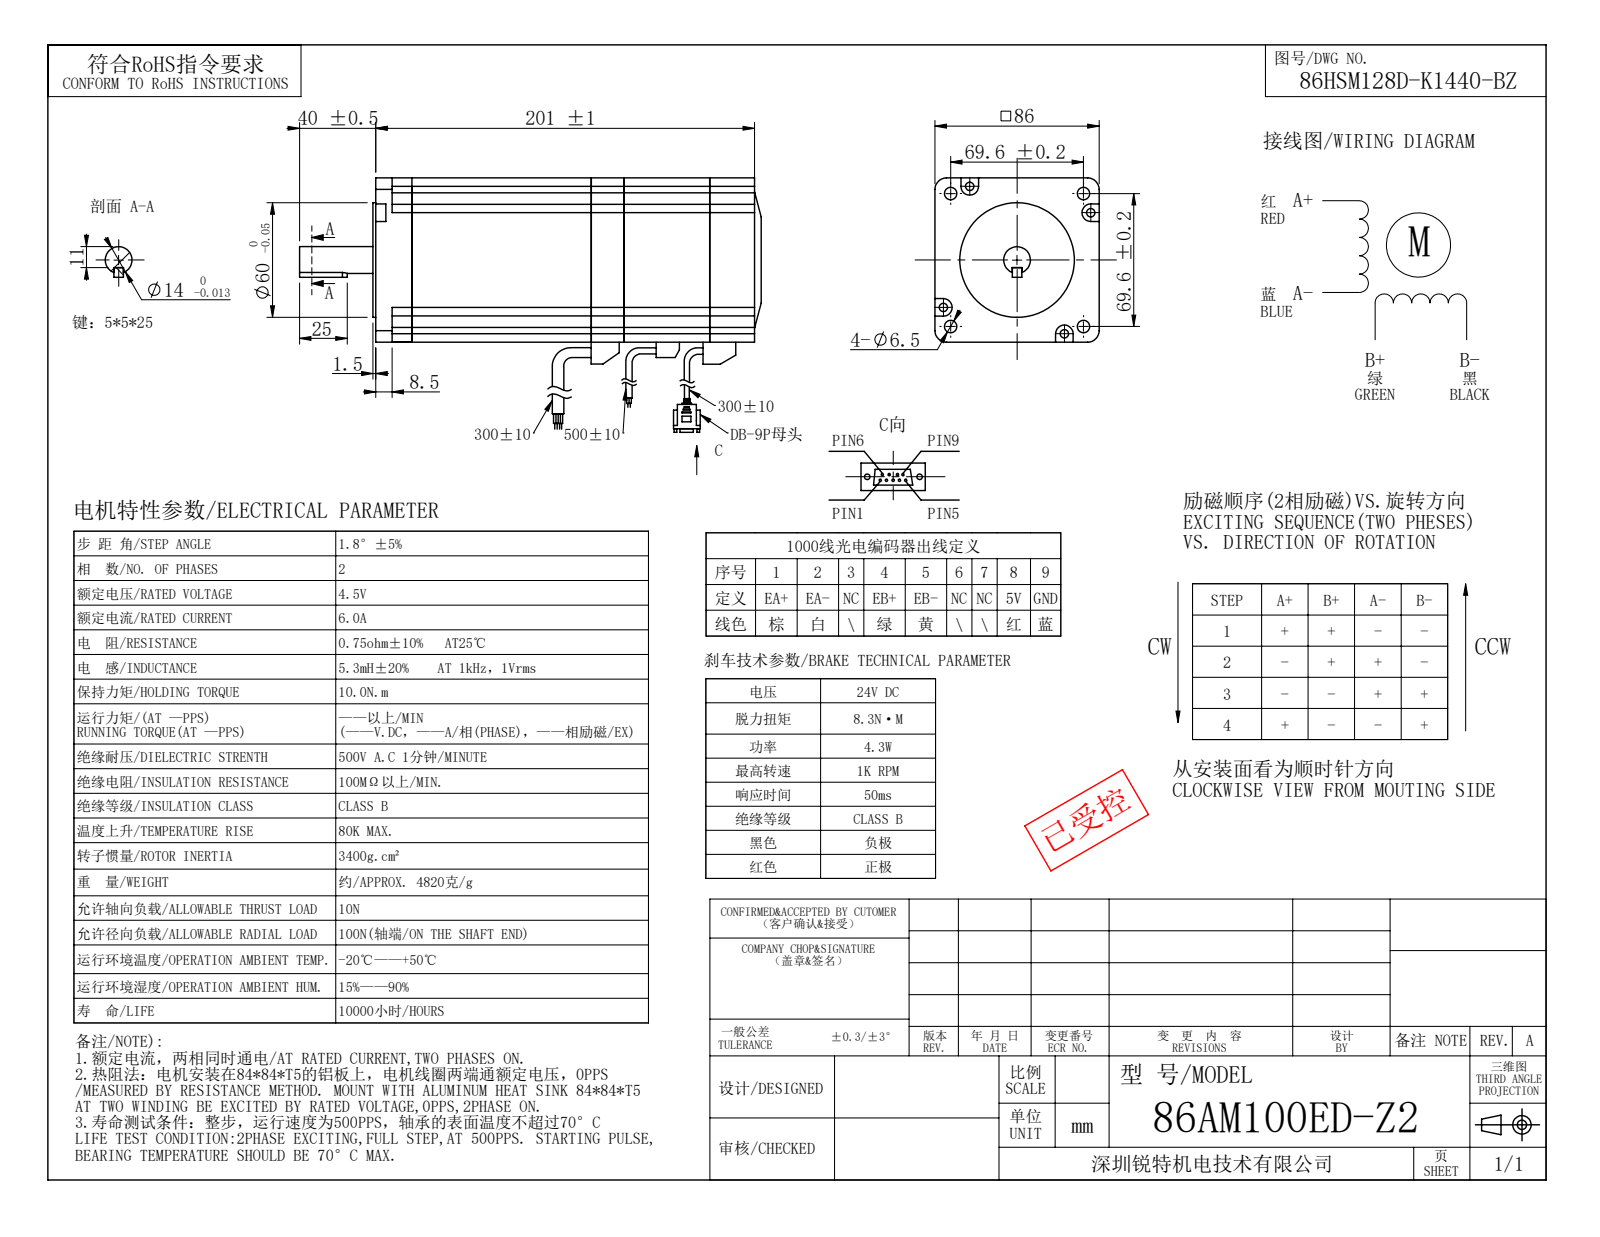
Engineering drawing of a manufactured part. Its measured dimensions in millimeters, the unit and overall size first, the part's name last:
Units: millimetres
Overall size (bounding box): 241.9 × 86 × 86
Round holes (diameter × count): ⌀2 ×4, ⌀3 ×4, ⌀4.4 ×4, ⌀6.5 ×4, ⌀13.6 ×1, ⌀26.2 ×1, ⌀40 ×1, ⌀80 ×1, ⌀80.8 ×1
Round bosses / shafts (diameter × count): ⌀60 ×1, ⌀52 ×1, ⌀14 ×1
Partial cylindrical surfaces — rounded edges, fillets, slot ends (radius × count): R1.9 ×9, R4.4 ×9, R4.6 ×4, R6 ×4, R6.05 ×4, R8.55 ×3, R1.97 ×2, R0.94 ×1
Main face-to-face distances: 86, 13.8, 72.2, 18.4, 174.9, 156.5, 8.5, 166.4, 148, 33
Hole centre spacings: 10.7, 45.88, 59.72, 64.88, 74.08, 94.55, 19.52, 49.21
Volume: 560 044 mm³ · Surface area: 169 996 mm²
Bodies: 6 solids, 307 faces (133 planar, 172 cylindrical, 2 other)
Part name (STEP PRODUCT): 86A8EC-Z键; 86A8EC-Z后端盖; 86A8EC-Z定子; 86A8EC-Z端盖 (+3 more)
STEP written by: SolidWorks 2023 (AUTOMOTIVE_DESIGN)
